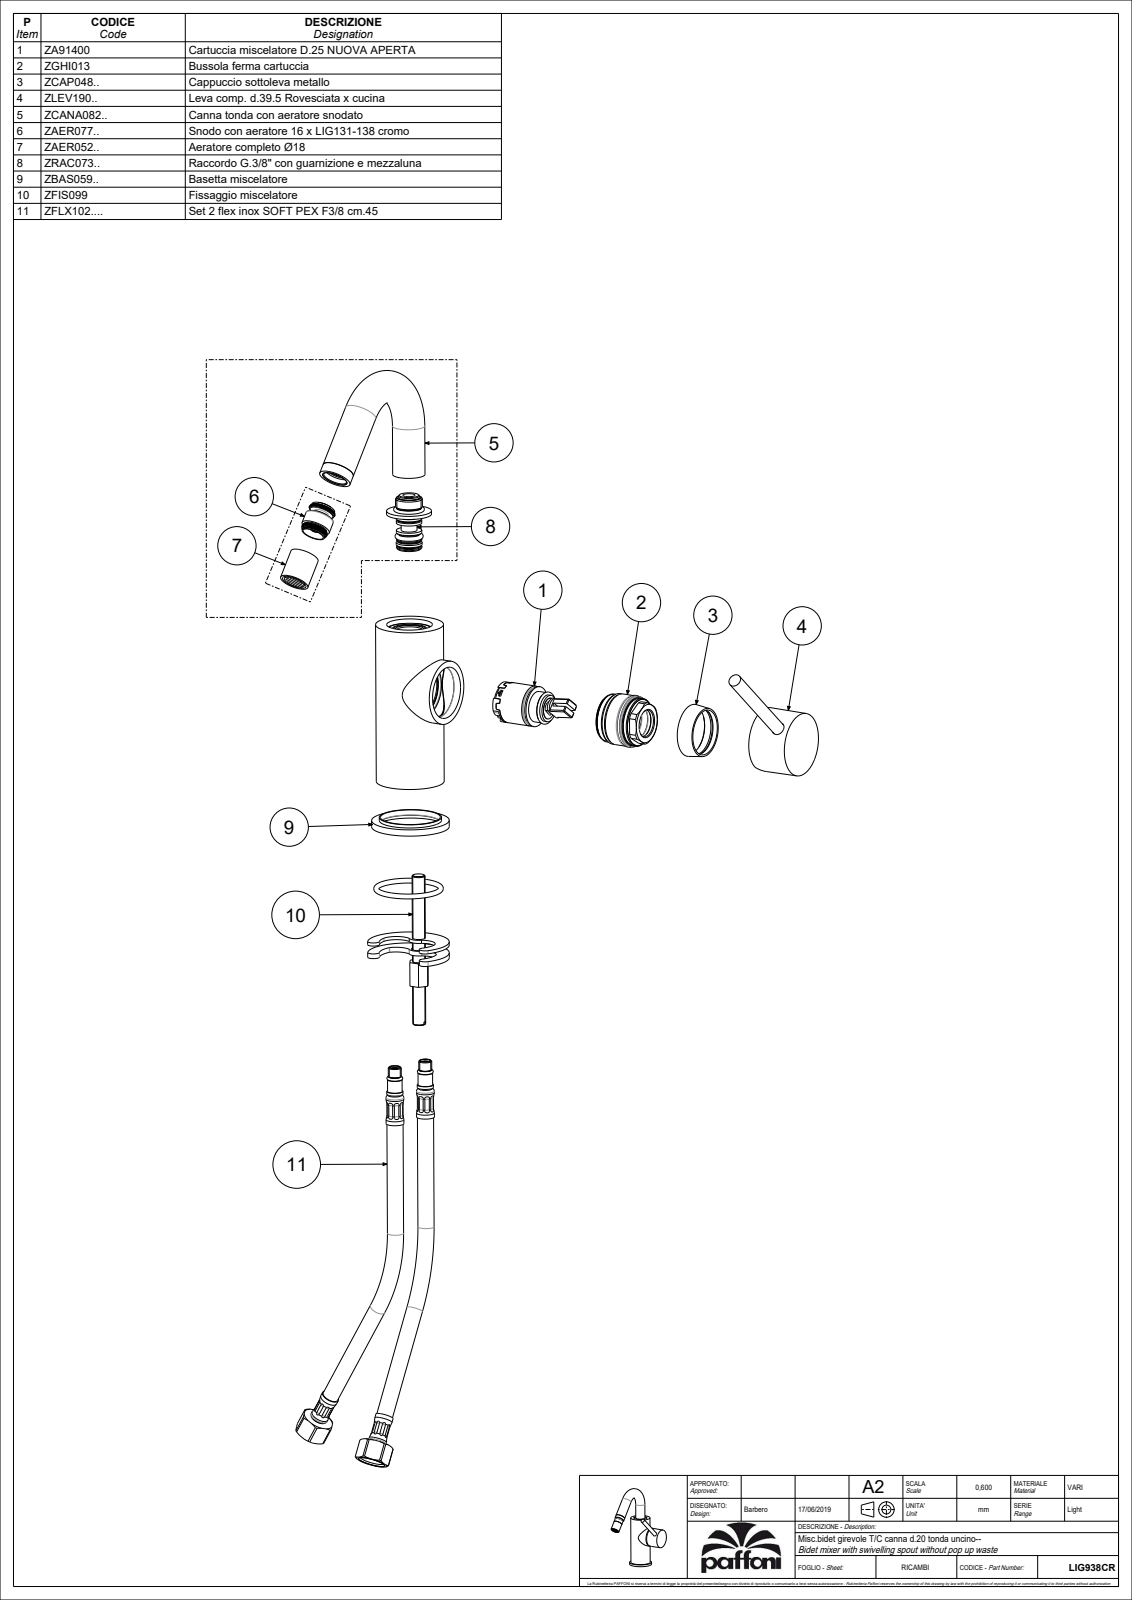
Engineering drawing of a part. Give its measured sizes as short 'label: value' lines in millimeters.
name: LIG938CR
written by: CREO PARAMETRIC BY PTC INC, 2020044 (CONFIG_CONTROL_DESIGN)
unit: mm
bodies: 0 solids, 123 faces (52 planar, 52 cylindrical, 19 other)
size: 175.5 × 132.16 × 79.15
holes: 1× ⌀3
bosses: 3× ⌀20, 1× ⌀48, 1× ⌀42, 1× ⌀39.5, 1× ⌀18, 1× ⌀10, 1× ⌀7.9, 1× ⌀7.6
rounds: 8× R1, 2× R0.8, 1× R3.5, 1× R5, 1× R6.4
face distances: 4, 104, 100, 10, 25.15, 15.15, 7.5, 1.5, 6, 0.5
